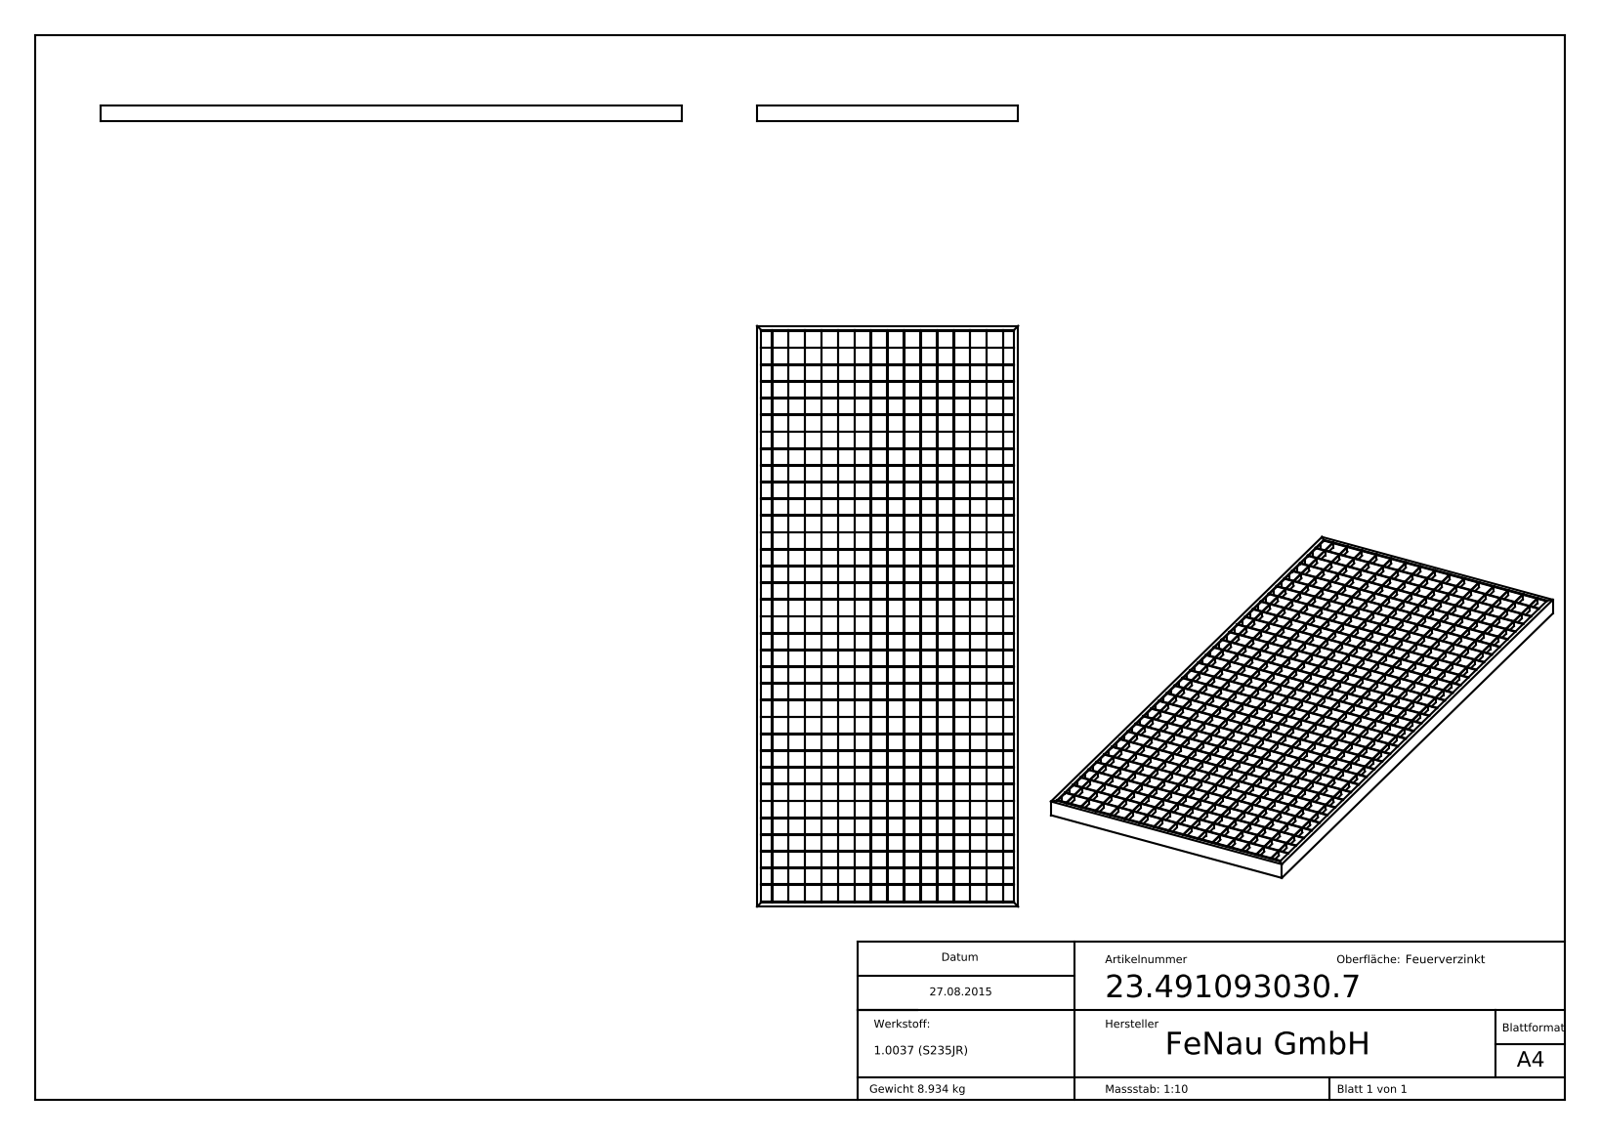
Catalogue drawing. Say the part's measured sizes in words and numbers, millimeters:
The part is named "23-491093030-7". Its 3-D file was written by "SolidWorks 2015 (CONFIG_CONTROL_DESIGN)". It is 1 solid with 1980 faces: 1980 planar, 0 cylindrical and 0 other. Overall it measures 1090 by 490 by 30 millimeters. Its volume is 1 145 000 cubic millimeters and its surface area 1 634 000 square millimeters. The main face-to-face distances are 63, 31.5, 94.5, 126, 157.5, 189, 220.5, 252, 31, 283.5.
